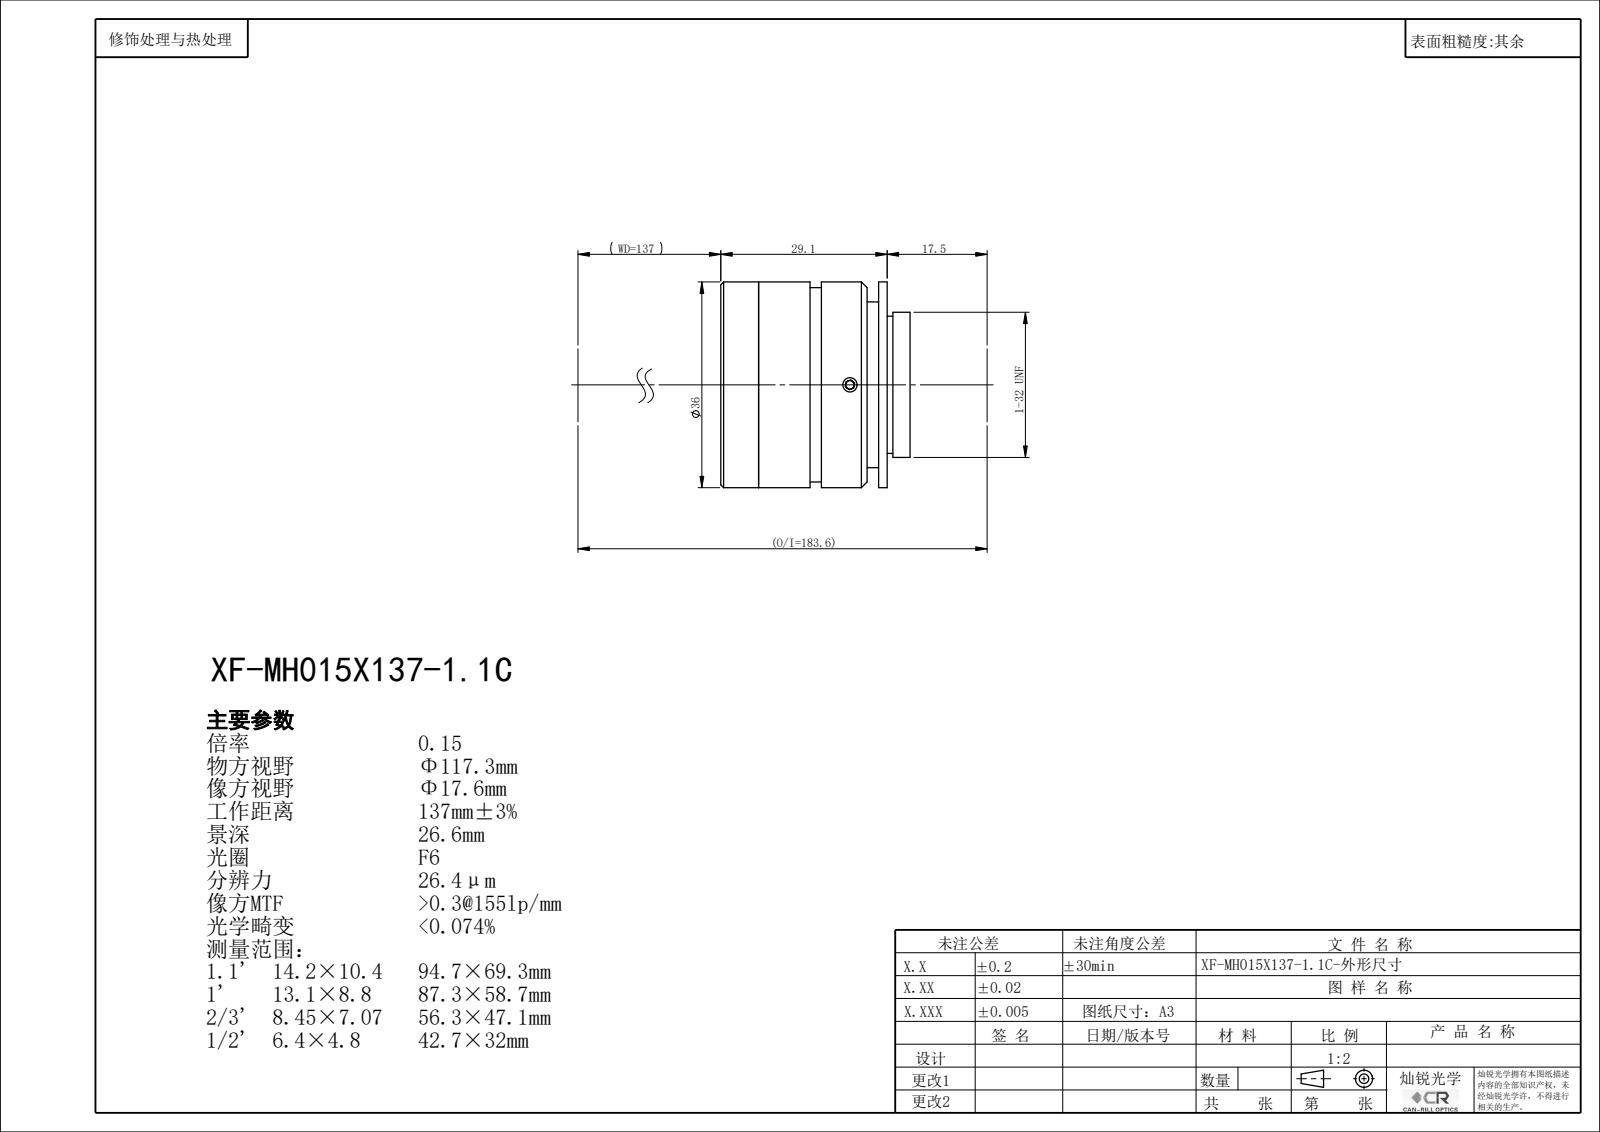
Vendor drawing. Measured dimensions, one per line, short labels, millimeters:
name: XF-MH015X137-1.1C
written by: SolidWorks 2022 (CONFIG_CONTROL_DESIGN)
unit: mm
bodies: 0 solids, 102 faces (47 planar, 34 cylindrical, 21 other)
size: 36 × 36 × 33.13
holes: 3× ⌀2.5, 1× ⌀10, 1× ⌀15, 1× ⌀17.4, 1× ⌀21.5, 1× ⌀24.9, 1× ⌀26
bosses: 1× ⌀36, 1× ⌀34, 1× ⌀29, 1× ⌀25.4, 1× ⌀24
face distances: 22.52, 6.62, 29.14, 1.5, 27.64, 21.02, 2.02, 3.52, 4.5, 2.12
